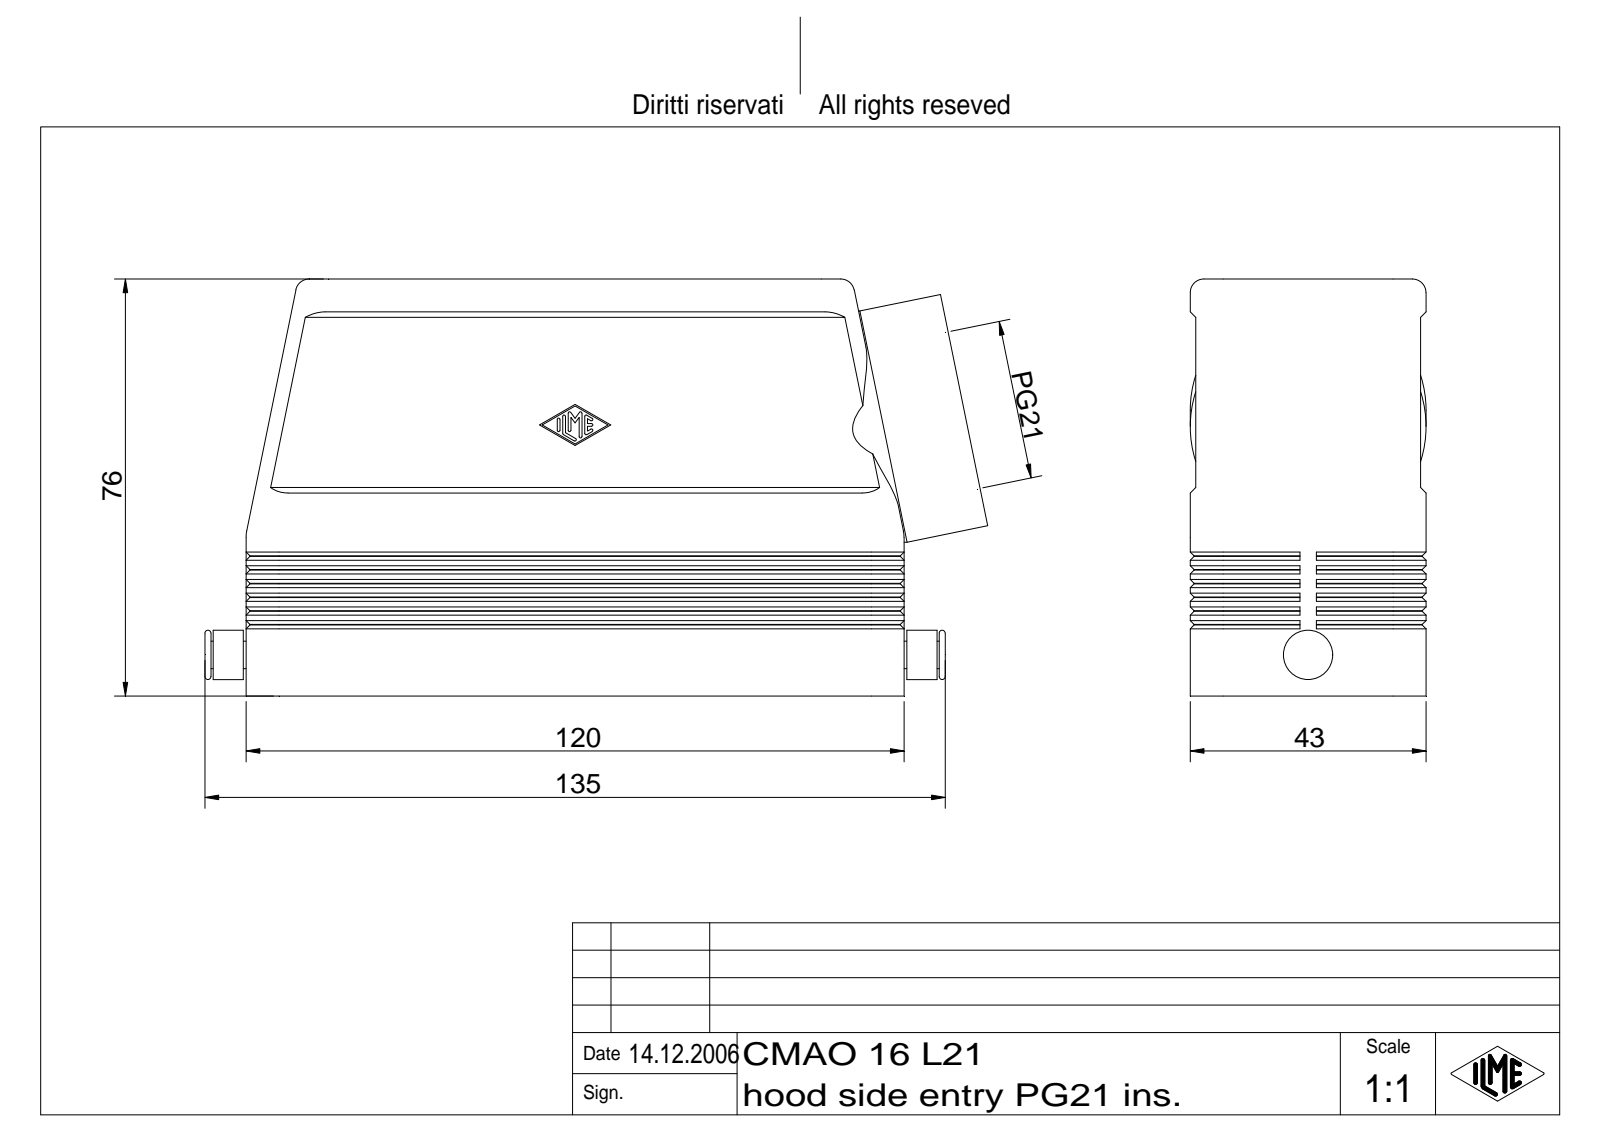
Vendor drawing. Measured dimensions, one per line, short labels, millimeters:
name: CH Tüllengehäuse für einen Einsatz Teil 5
written by: Autodesk Inventor 7 (AUTOMOTIVE_DESIGN)
unit: mm
bodies: 1 solid, 534 faces (194 planar, 136 cylindrical, 204 other)
size: 142.74 × 76 × 43
volume: 97 868 mm³; area: 58 102 mm²
holes: 1× ⌀24.78, 1× ⌀26.78
bosses: 1× ⌀43, 1× ⌀9, 1× ⌀5
rounds: 14× R0.25, 10× R6, 4× R2, 4× R2.5, 4× R3, 2× R5.3
face distances: 3, 37, 40, 1, 2, 42, 39, 43, 41, 1.77
